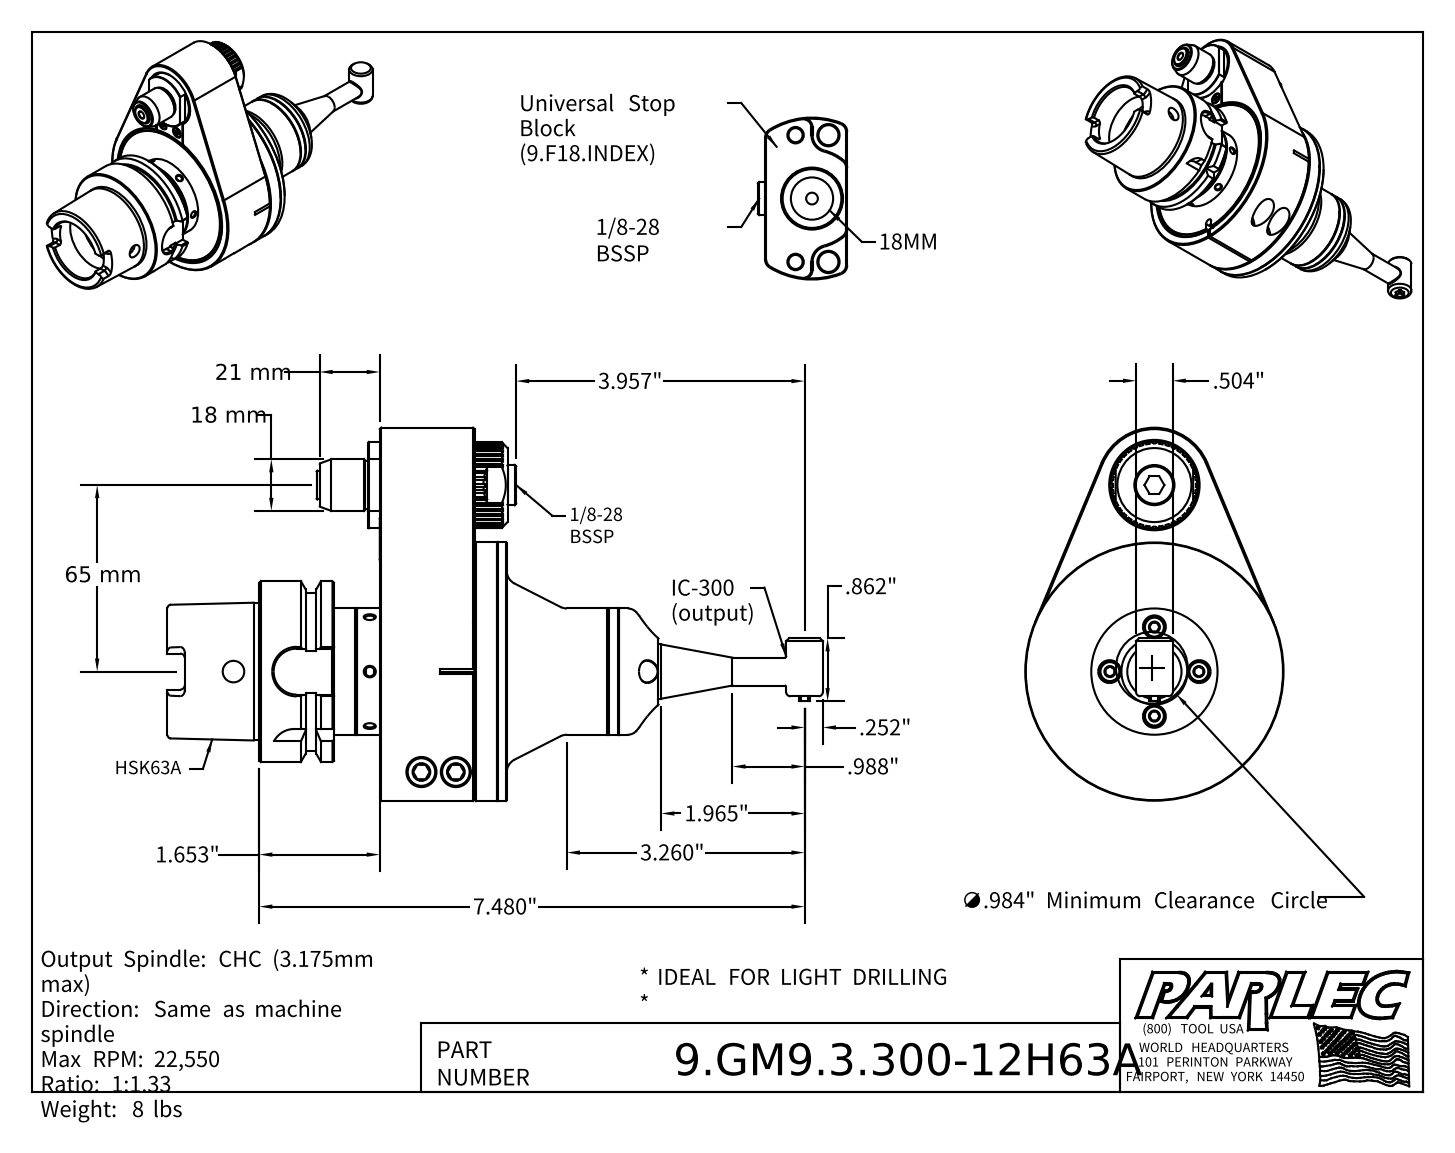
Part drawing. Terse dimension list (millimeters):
name: 9.GM9.3.300-12H63A
written by: Autodesk Inventor 2022 (AUTOMOTIVE_DESIGN)
unit: mm
bodies: 2 solids, 766 faces (374 planar, 204 cylindrical, 188 other)
size: 228.4 × 130 × 90
volume: 469 024 mm³; area: 109 768 mm²
holes: 5× ⌀7.5, 4× ⌀3.3, 3× ⌀4.2, 2× ⌀4, 2× ⌀6, 2× ⌀7, 2× ⌀10.5, 2× ⌀13, 1× ⌀5, 1× ⌀5.5, 1× ⌀6.5, 1× ⌀8.4
bosses: 5× ⌀7, 4× ⌀10, 2× ⌀12.8, 2× ⌀6, 2× ⌀5.8, 1× ⌀90, 1× ⌀82, 1× ⌀78
rounds: 5× R3, 4× R8, 2× R0.85, 2× R1.5, 2× R2, 2× R2.15, 1× R2.35, 1× R14.9
face distances: 24.5, 3, 49, 33, 8.5, 44.2, 41.2, 30, 11.2, 16
hole spacings: 15.5, 21.92, 13, 46.1, 5.1, 16.35, 20.74, 30.01
